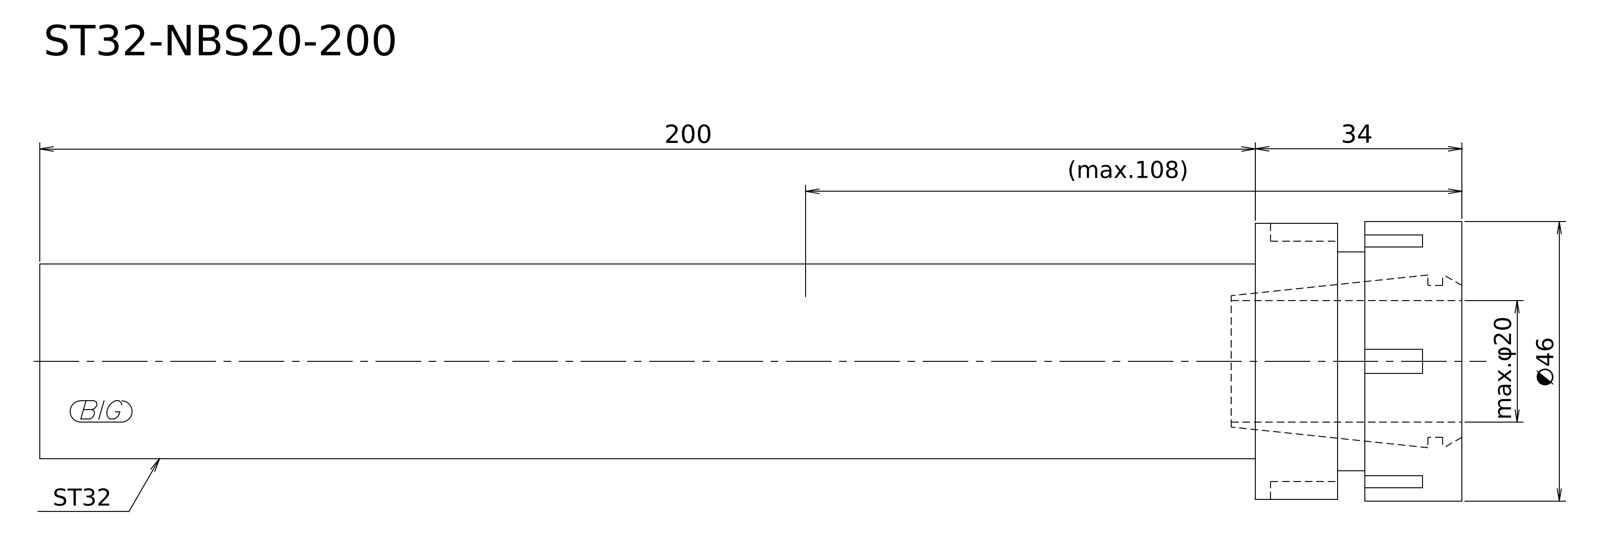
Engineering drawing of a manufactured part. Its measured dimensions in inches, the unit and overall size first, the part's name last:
Units: inches
Overall size (bounding box): 9.213 × 1.811 × 1.811
Round bosses / shafts (diameter × count): ⌀1.811 ×1, ⌀1.791 ×1, ⌀1.417 ×1, ⌀1.26 ×1
Main face-to-face distances: 1.339, 9.213, 7.874, 0.63, 0.709, 8.583, 0.807, 0.177, 0.531, 8.406
Volume: 13.06 in³ · Surface area: 45.57 in²
Bodies: 1 solid, 9 faces (5 planar, 4 cylindrical, 0 other)
STEP written by: Kubotek KeyCreator V8.5.1 (14335) (CONFIG_CONTROL_DESIGN)
